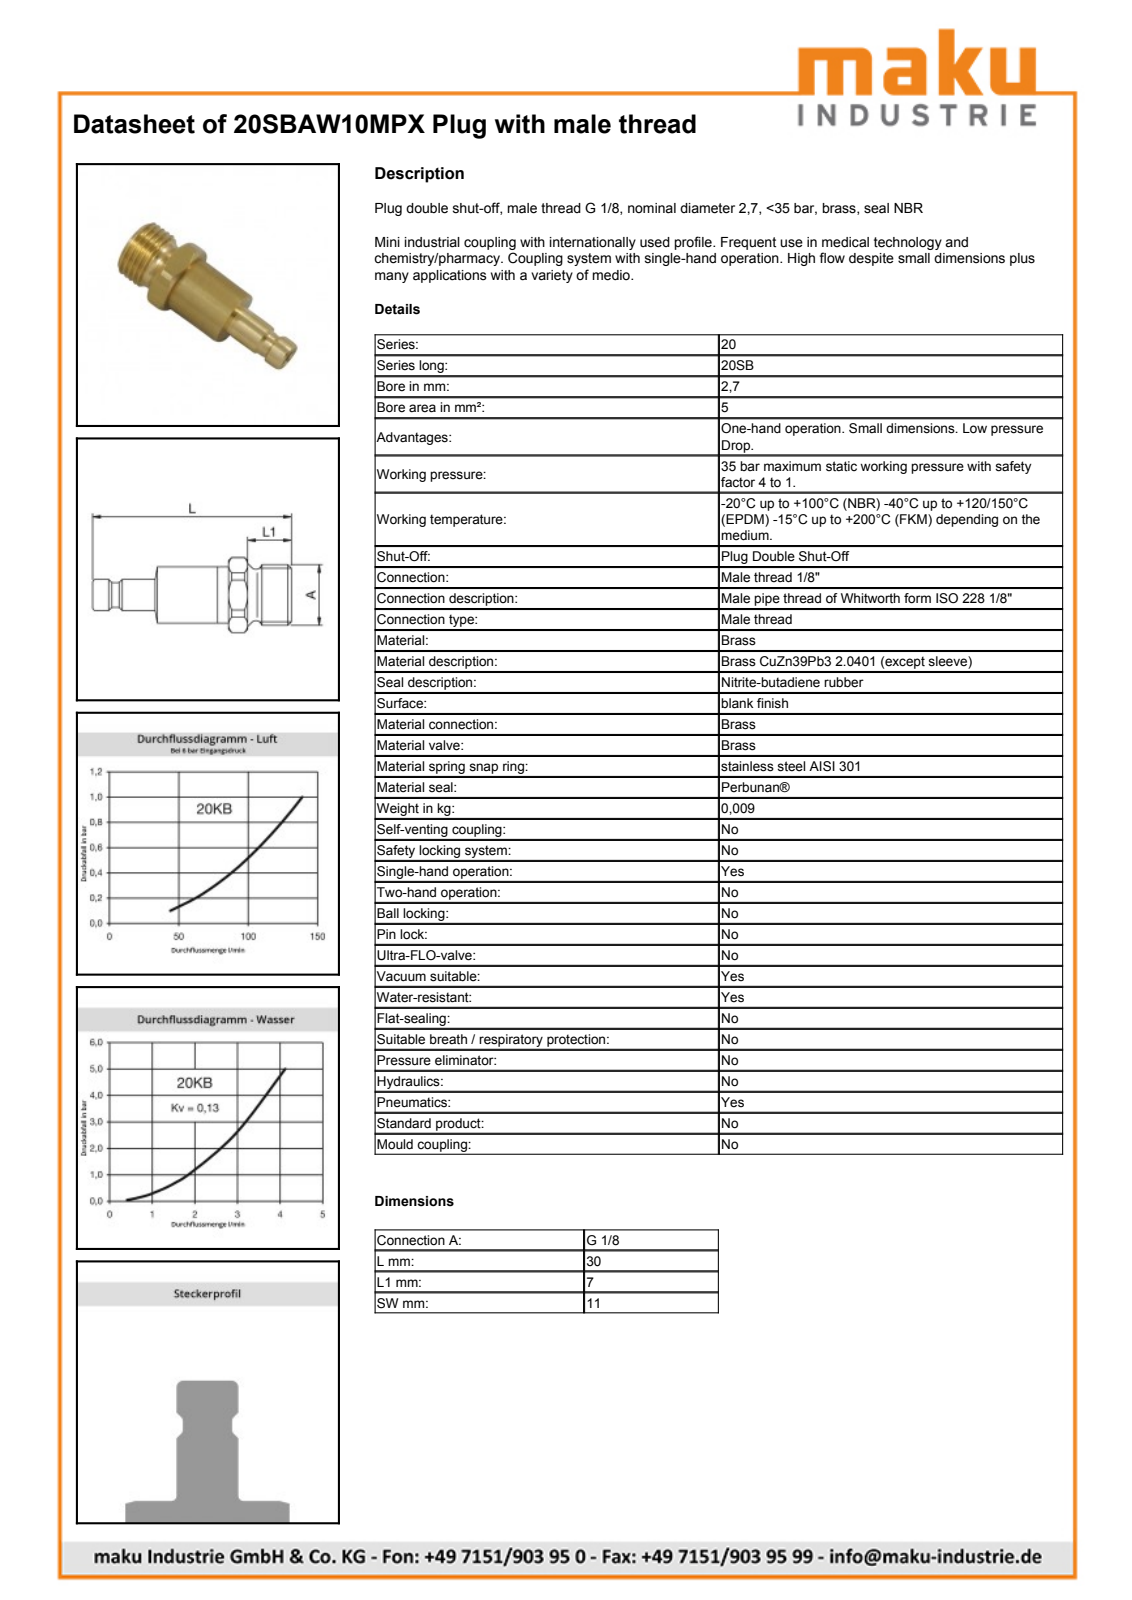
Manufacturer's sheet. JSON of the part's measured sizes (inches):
{"part_name": "D105900", "step_written_by": "Autodesk Inventor 2011 (AUTOMOTIVE_DESIGN)", "units": "inches", "bodies": {"solids": 1, "faces": 55, "planar": 12, "cylindrical": 16, "other": 27}, "overall_size": [1.183, 0.472, 0.452], "volume_in3": 0.096, "surface_area_in2": 1.717, "round_holes": [[0.315, 1], [0.319, 1]], "round_bosses_or_shafts": [[0.383, 1], [0.354, 1], [0.287, 1], [0.268, 1], [0.197, 1], [0.156, 1]], "partial_cylinders_radius": [[0.236, 1]], "face_to_face_distances": [0.396, 0.433, 0.12, 0.276, 0.787, 0.907, 1.183, 0.612, 0.175, 0.295]}
